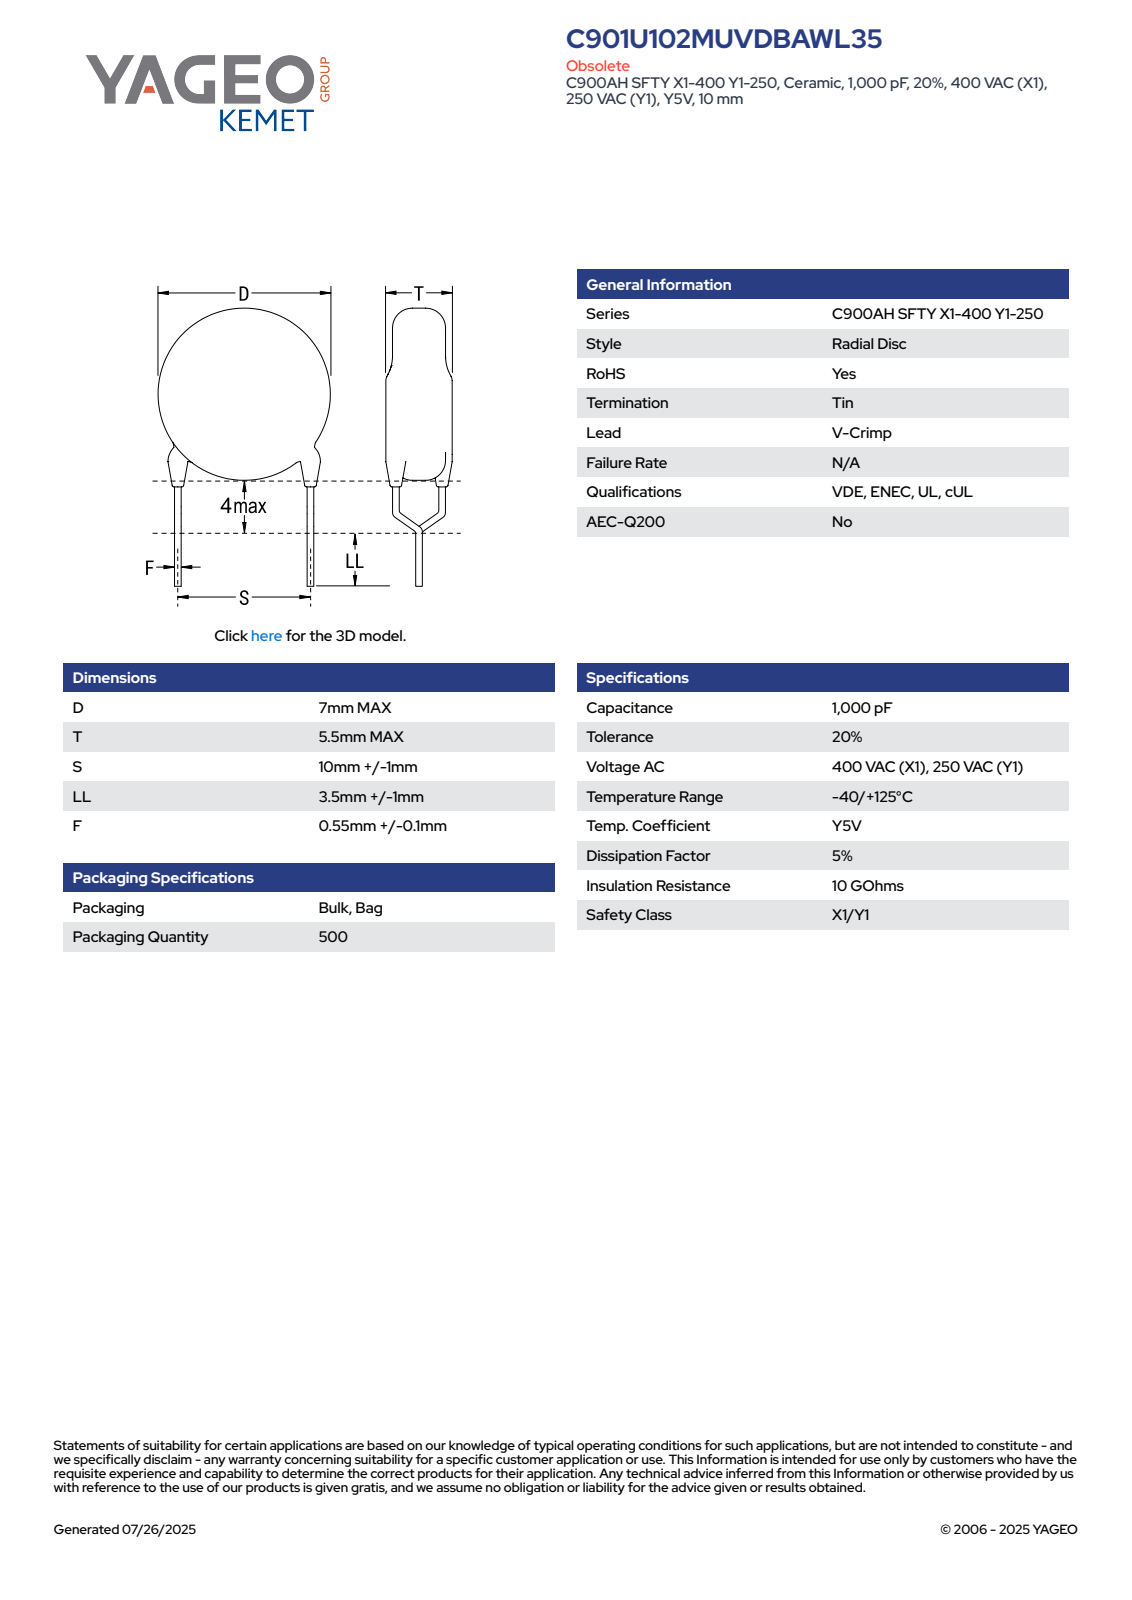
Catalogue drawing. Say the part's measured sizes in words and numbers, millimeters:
The part is named "CCD_VCC900_D7T5.5S10LL4.5F0.65". Its 3-D file was written by "SolidWorks 2014 (AUTOMOTIVE_DESIGN)". It is 5 solids with 93 faces: 65 planar, 16 cylindrical and 12 other. Overall it measures 15.3 by 10.65 by 5.5 millimeters. Its volume is 214 cubic millimeters and its surface area 236 square millimeters. Round bosses or shafts: 6 of diameter 0.65, 1 of diameter 7. The main face-to-face distances are 5.5, 7.4, 0.91, 12.25, 4.85, 11.34, 3.94, 3.71, 0.34, 1.87.
